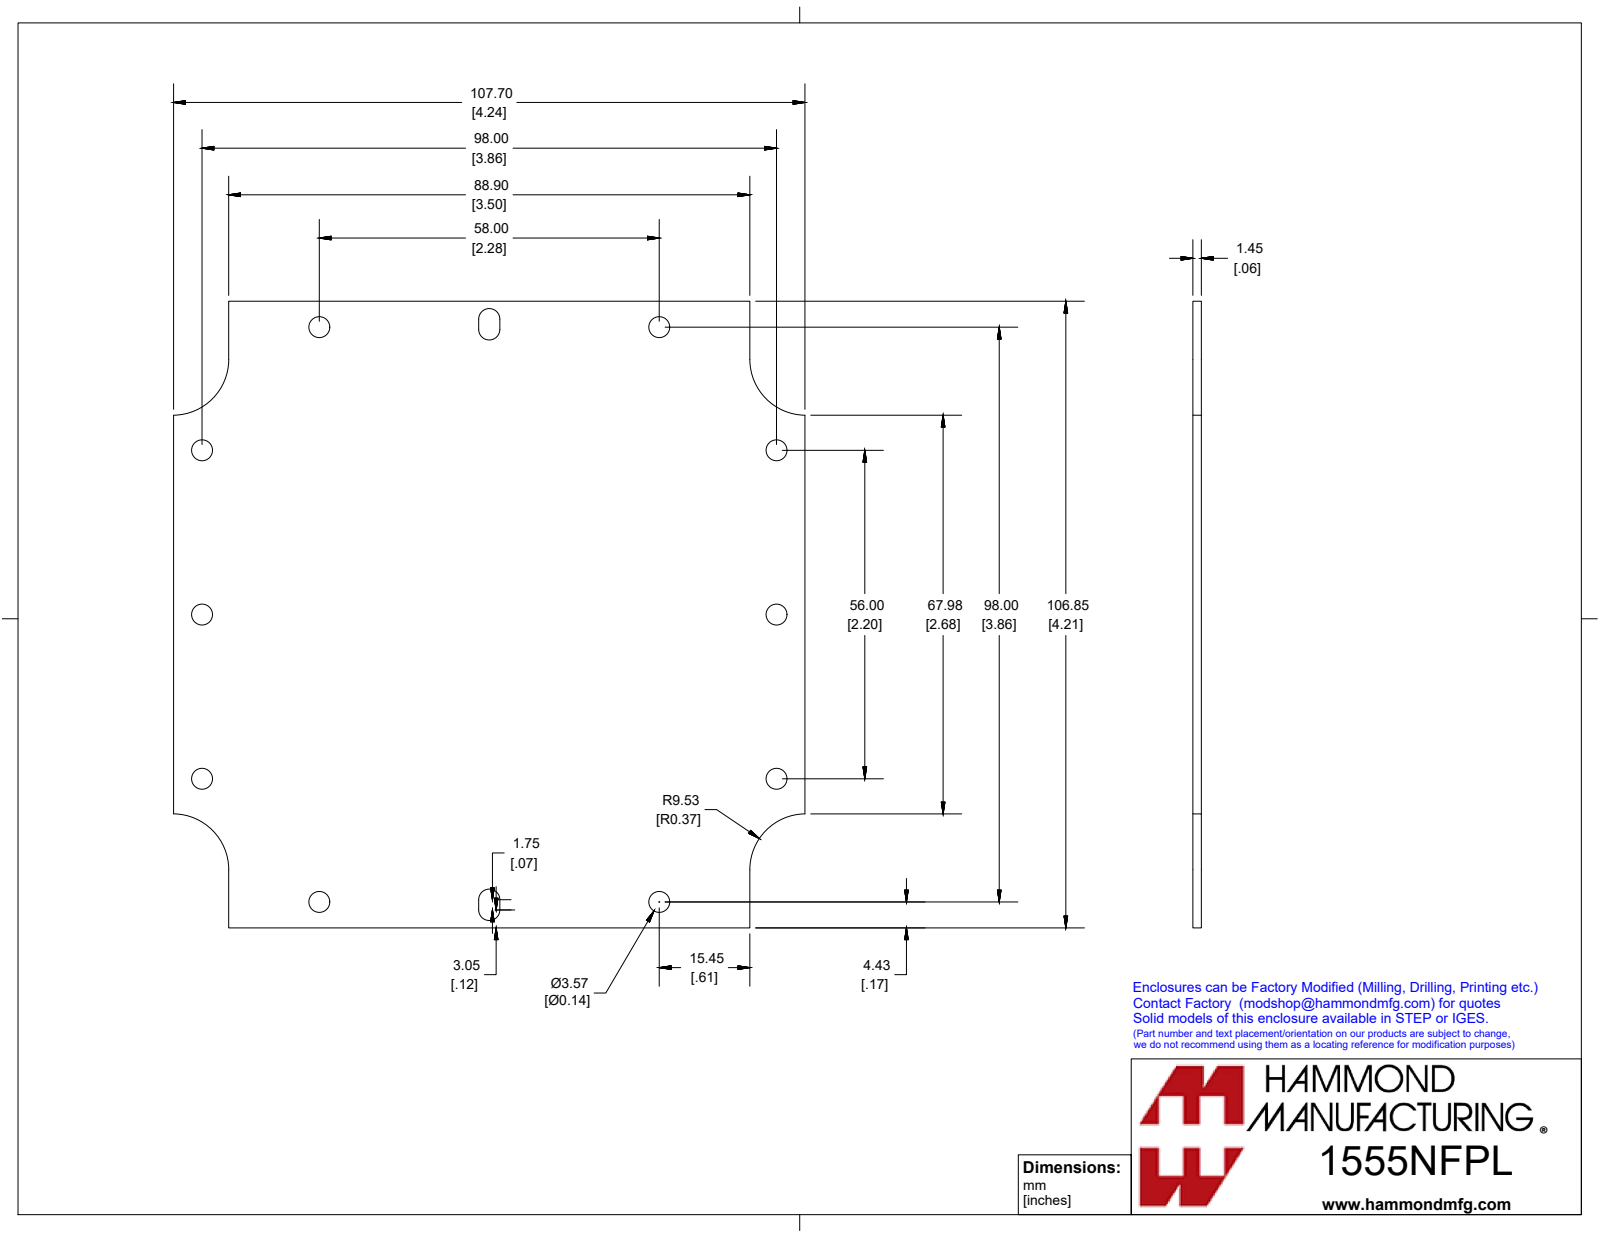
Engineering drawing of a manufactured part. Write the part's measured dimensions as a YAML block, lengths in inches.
part_name: "1555NFPL"
step_written_by: "SolidWorks 2019 (CONFIG_CONTROL_DESIGN)"
units: inches
bodies: {solids: 1, faces: 32, planar: 14, cylindrical: 18, other: 0}
overall_size: [4.24, 4.207, 0.057]
volume: 0.947
surface_area: 34.48
round_holes:
  - {diameter: 0.141, count: 10}
partial_cylinders:
  - {radius: 0.071, count: 4}
  - {radius: 0.375, count: 4}
face_to_face_distances: [0.057, 4.206, 4.24, 0.37, 3.87, 3.5, 2.049, 2.191, 1.679, 1.821]
hole_center_spacings: [3.858, 1.102, 1.142, 2.083, 3.132, 3.18, 3.626, 4.013]
